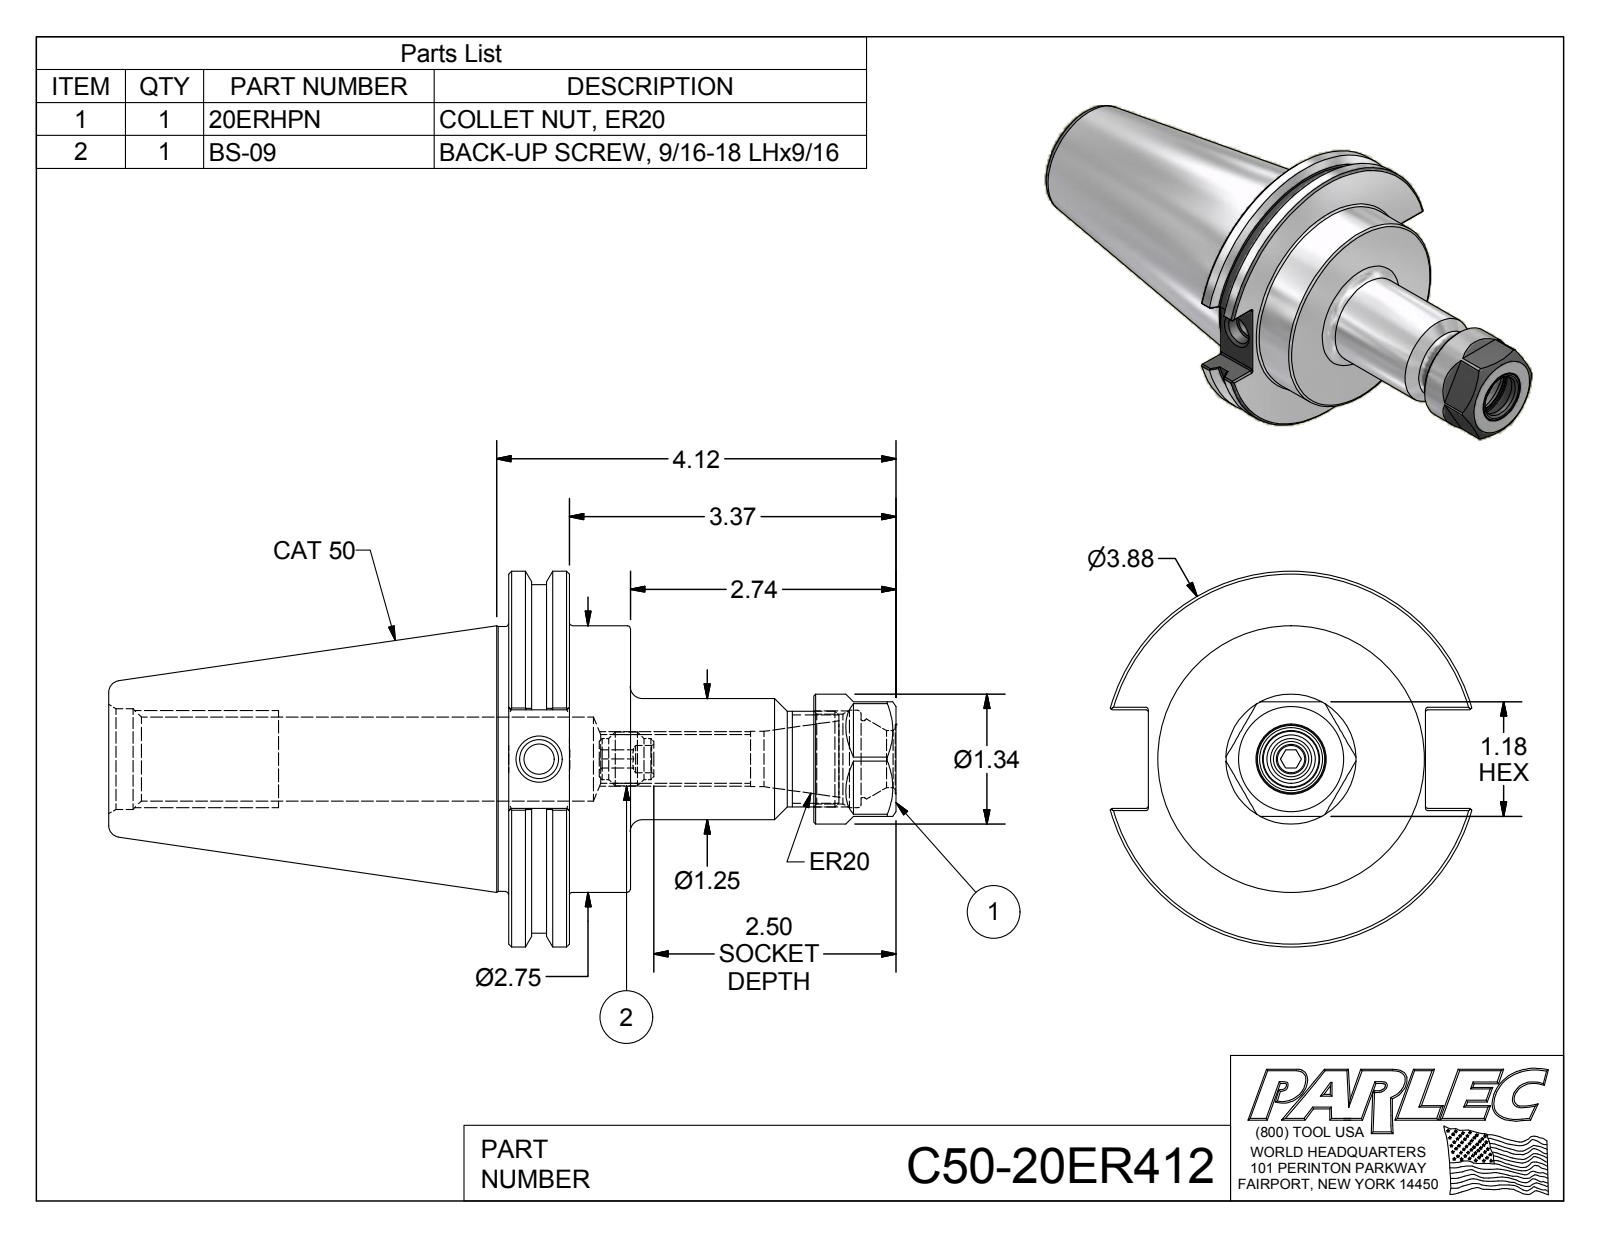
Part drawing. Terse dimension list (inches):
name: C50-20ER412; C50-20ER4-1; 20ERHPN; BS-09
written by: Autodesk Inventor 2012 (AUTOMOTIVE_DESIGN)
unit: in
bodies: 3 solids, 150 faces (63 planar, 37 cylindrical, 50 other)
size: 8.12 × 3.875 × 3.729
volume: 25.37 in³; area: 95.34 in²
holes: 1× ⌀0.281, 1× ⌀0.315, 1× ⌀0.399, 1× ⌀0.502, 1× ⌀0.57, 1× ⌀0.587, 1× ⌀0.79, 1× ⌀0.865, 1× ⌀0.926, 1× ⌀1.005, 1× ⌀1.038
bosses: 1× ⌀3.875, 1× ⌀3.594, 1× ⌀2.75, 1× ⌀2.73, 1× ⌀1.34, 1× ⌀1.25, 1× ⌀0.984, 1× ⌀0.555
rounds: 12× R0.02
face distances: 0.625, 1.255, 0.63, 1.18, 3.145, 2.52, 1.89, 3.995, 3.37, 2.74
